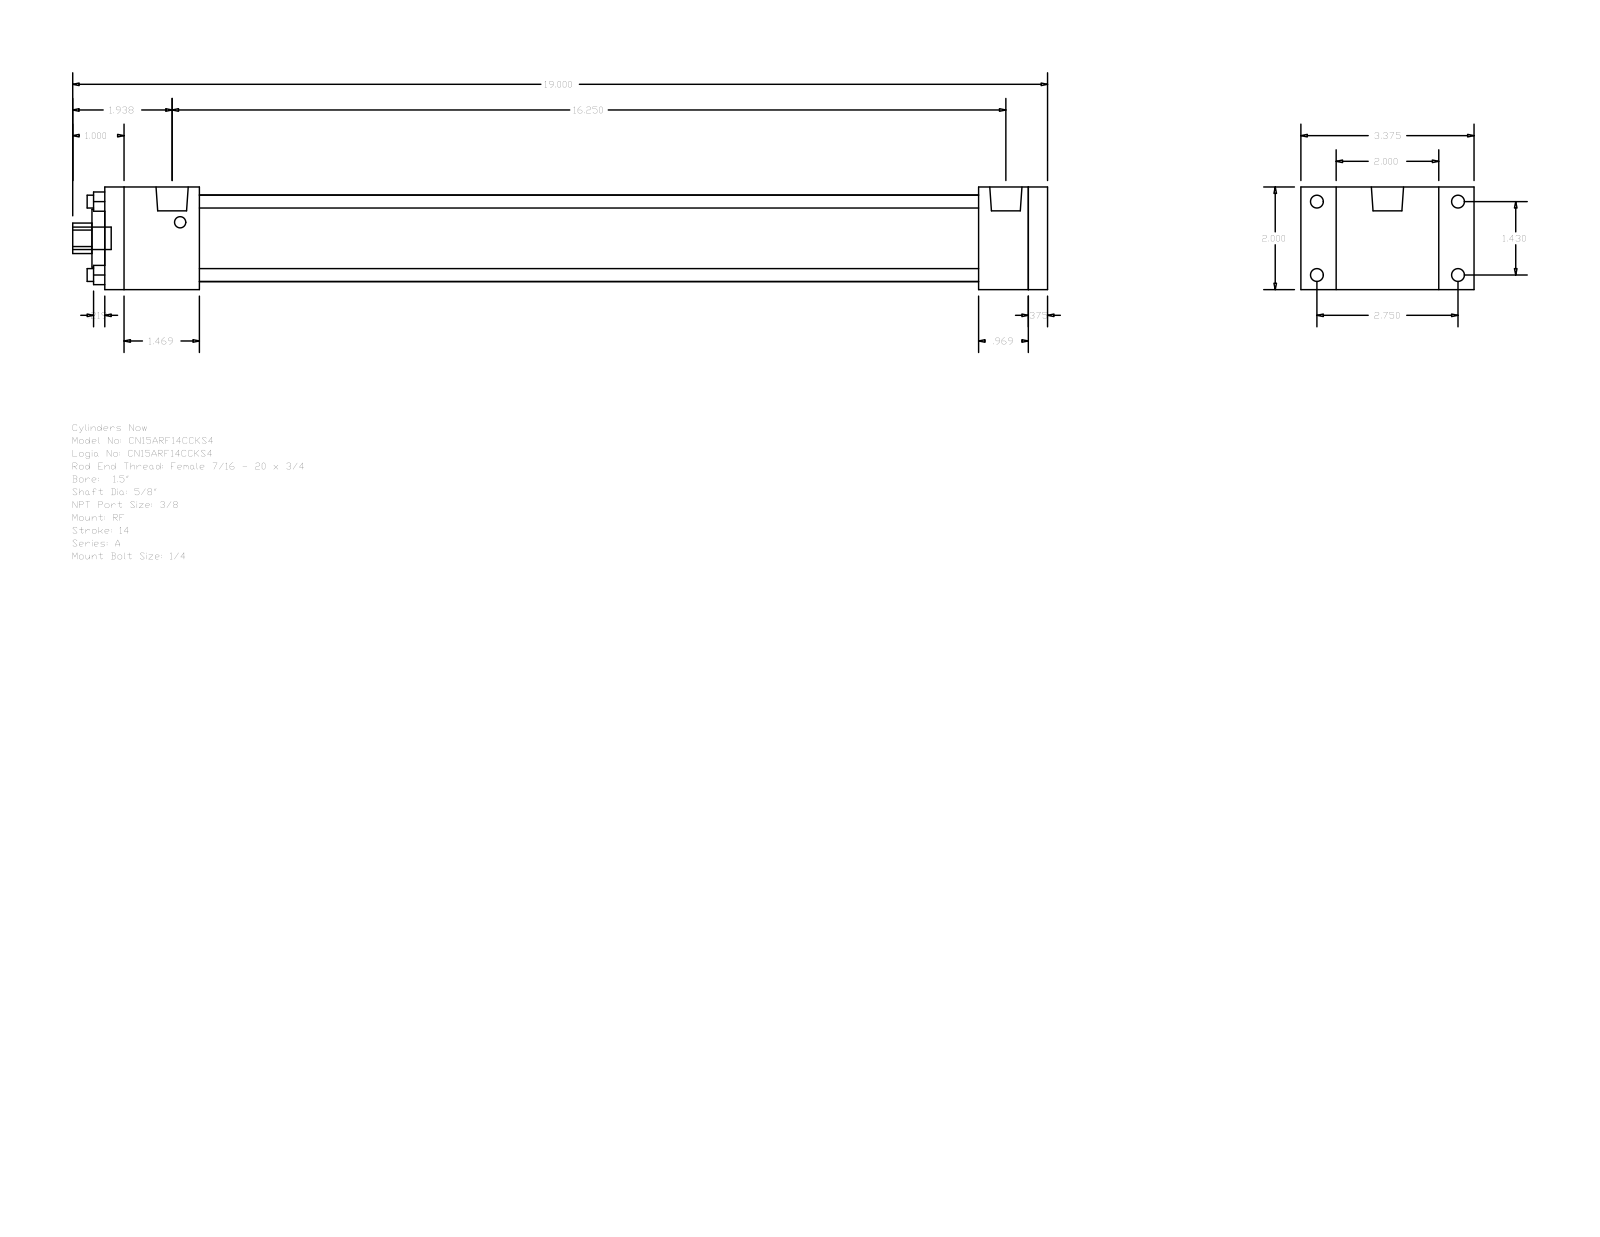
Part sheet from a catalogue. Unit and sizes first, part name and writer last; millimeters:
Units: millimetres
Overall size (bounding box): 482.6 × 85.72 × 50.8
Round holes (diameter × count): ⌀6.35 ×4, ⌀15.88 ×1, ⌀28.57 ×1, ⌀42.93 ×1
Round bosses / shafts (diameter × count): ⌀6.35 ×4, ⌀5.56 ×4, ⌀15.93 ×2, ⌀11.11 ×1
Partial cylindrical surfaces — rounded edges, fillets, slot ends (radius × count): R7.54 ×1
Main face-to-face distances: 50.8, 9.53, 466.72, 457.19, 432.59, 24.6, 34.13, 46.83, 385.76, 410.36
Hole centre spacings: 25.68, 36.32, 51.36
Bodies: 0 solids, 92 faces (64 planar, 28 cylindrical, 0 other)
Part name (STEP PRODUCT): A_RF__0150_0.625
STEP written by: GSSL Pune (CONFIG_CONTROL_DESIGN)
